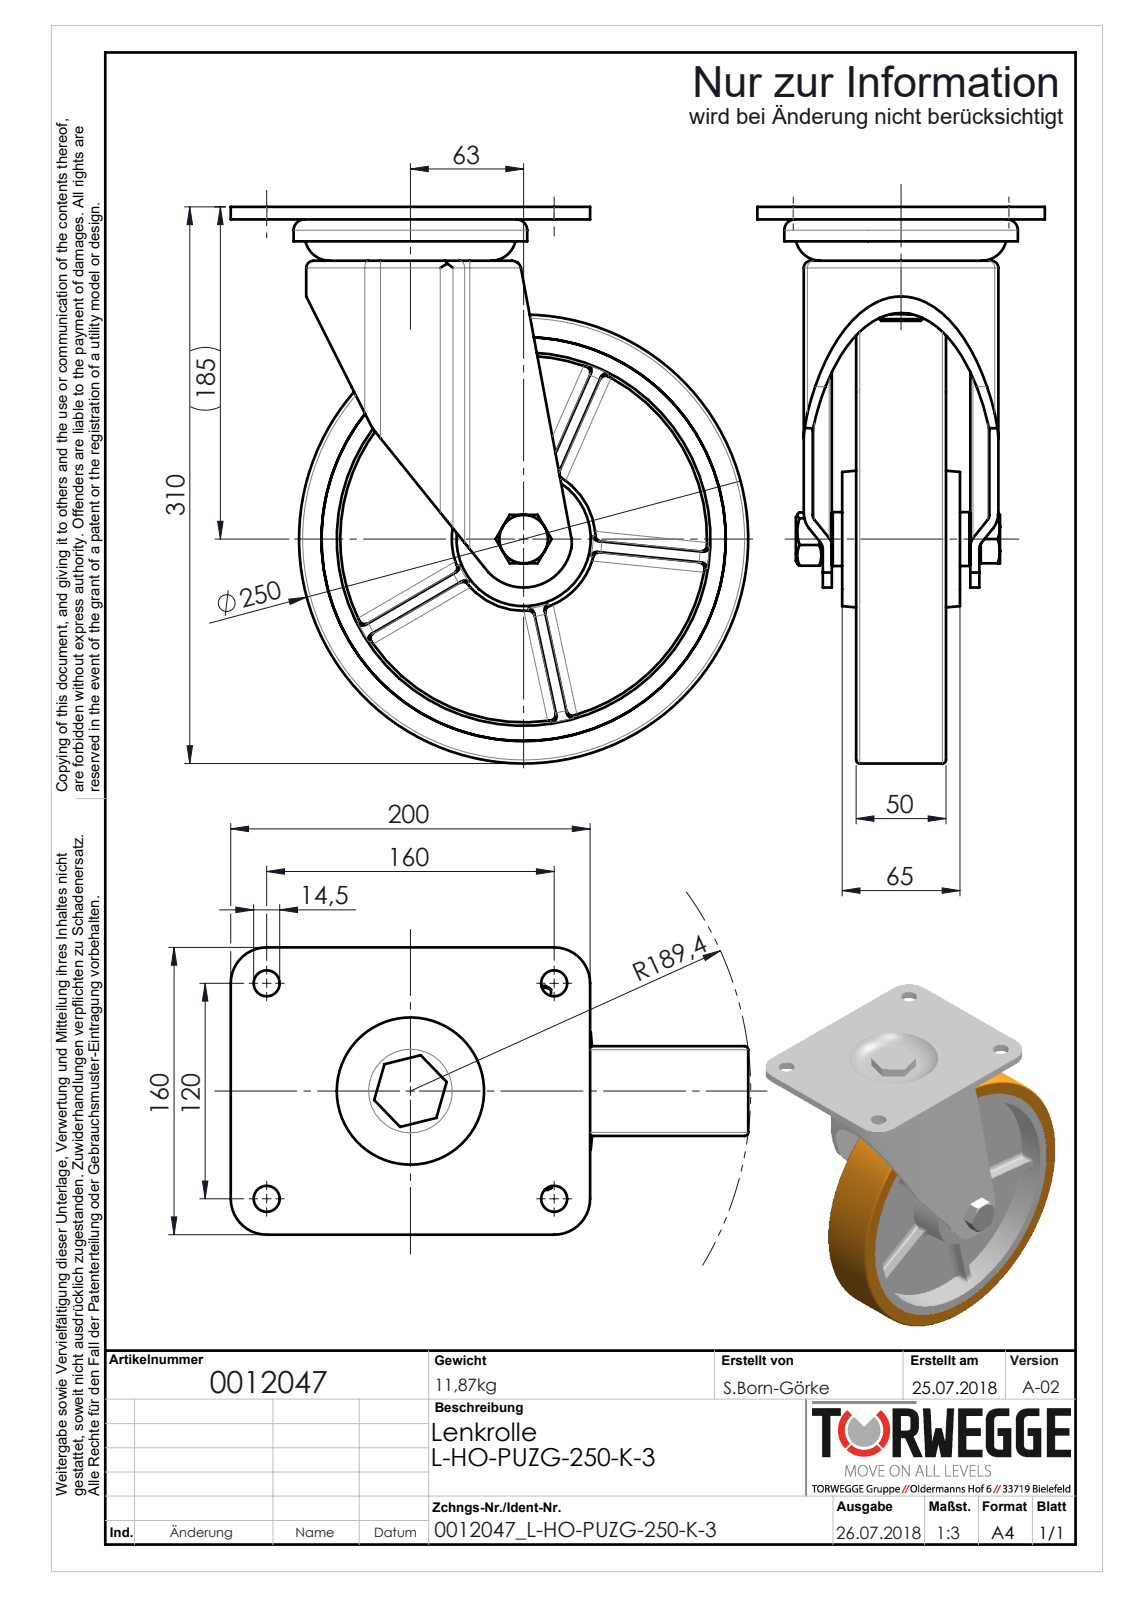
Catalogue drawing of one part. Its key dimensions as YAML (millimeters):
part_name: "0012047_L-HO-PUZG-250-K-3"
step_written_by: "SolidWorks 2018 (AUTOMOTIVE_DESIGN)"
units: millimeters
bodies: {solids: 0, faces: 598, planar: 166, cylindrical: 197, other: 235}
overall_size: [310, 288, 160]
round_holes:
  - {diameter: 14.5, count: 4}
  - {diameter: 52, count: 2}
  - {diameter: 15.29, count: 1}
  - {diameter: 18.3, count: 1}
  - {diameter: 18.5, count: 1}
  - {diameter: 24, count: 1}
  - {diameter: 24.5, count: 1}
  - {diameter: 24.6, count: 1}
  - {diameter: 25, count: 1}
  - {diameter: 32.15, count: 1}
  - {diameter: 32.16, count: 1}
  - {diameter: 38, count: 1}
round_bosses_or_shafts:
  - {diameter: 250, count: 1}
  - {diameter: 130, count: 1}
  - {diameter: 117.57, count: 1}
  - {diameter: 75, count: 1}
  - {diameter: 71.5, count: 1}
  - {diameter: 60.97, count: 1}
  - {diameter: 33.8, count: 1}
  - {diameter: 30, count: 1}
partial_cylinders:
  - {radius: 5, count: 23}
  - {radius: 4, count: 8}
  - {radius: 20, count: 6}
  - {radius: 3, count: 4}
  - {radius: 10, count: 2}
  - {radius: 34.5, count: 2}
  - {radius: 53.36, count: 2}
  - {radius: 58, count: 2}
face_to_face_distances: [5, 7, 5.56, 22.22, 27.78, 18.55, 40.77, 46.33, 68.55, 22]
hole_center_spacings: [100, 120, 160, 200]
